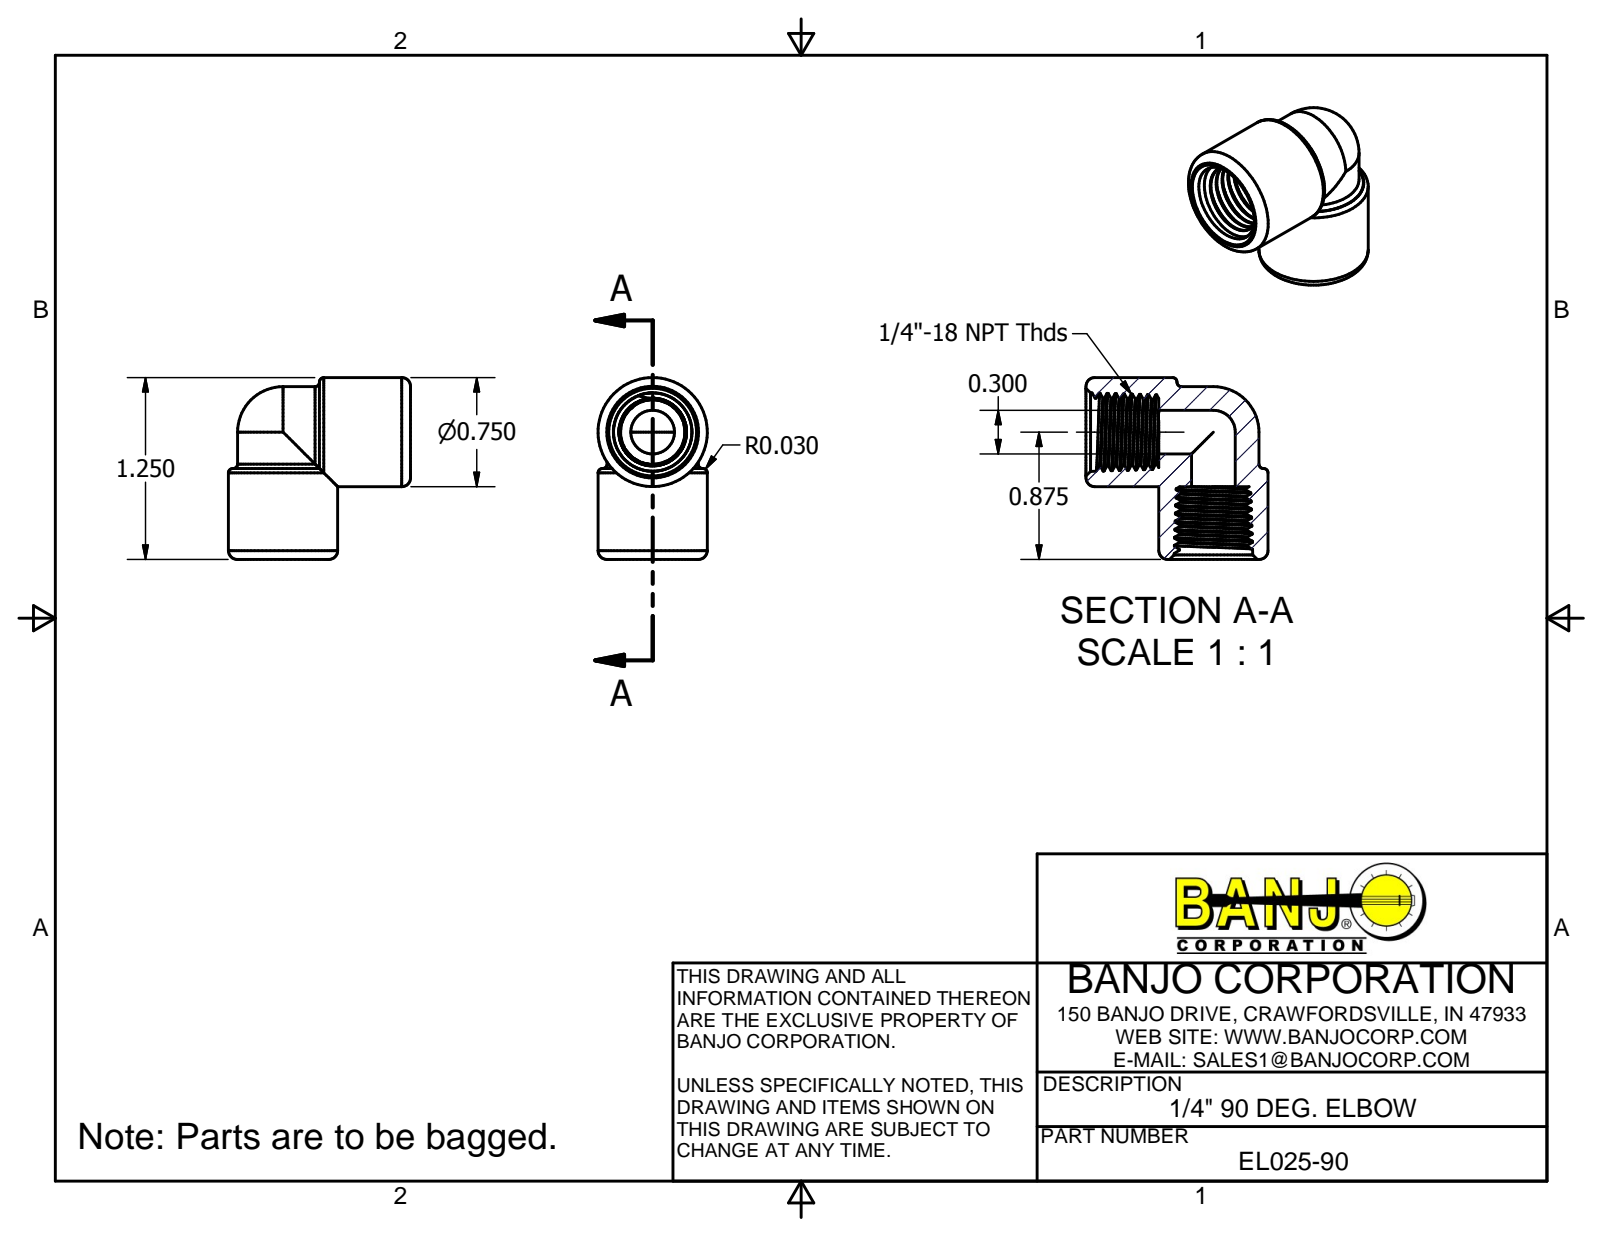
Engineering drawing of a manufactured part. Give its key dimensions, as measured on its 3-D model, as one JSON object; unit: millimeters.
{"part_name": "EL025-90", "step_written_by": "Autodesk Inventor 2014 (AUTOMOTIVE_DESIGN)", "units": "millimeters", "bodies": {"solids": 1, "faces": 51, "planar": 6, "cylindrical": 8, "other": 37}, "overall_size": [31.75, 31.75, 19.05], "volume_mm3": 7243, "surface_area_mm2": 4898, "round_holes": [[7.62, 2]], "round_bosses_or_shafts": [[19.05, 2]], "partial_cylinders_radius": [[7.78, 2], [7.94, 2]], "face_to_face_distances": [12.7, 3.17, 15.87]}
